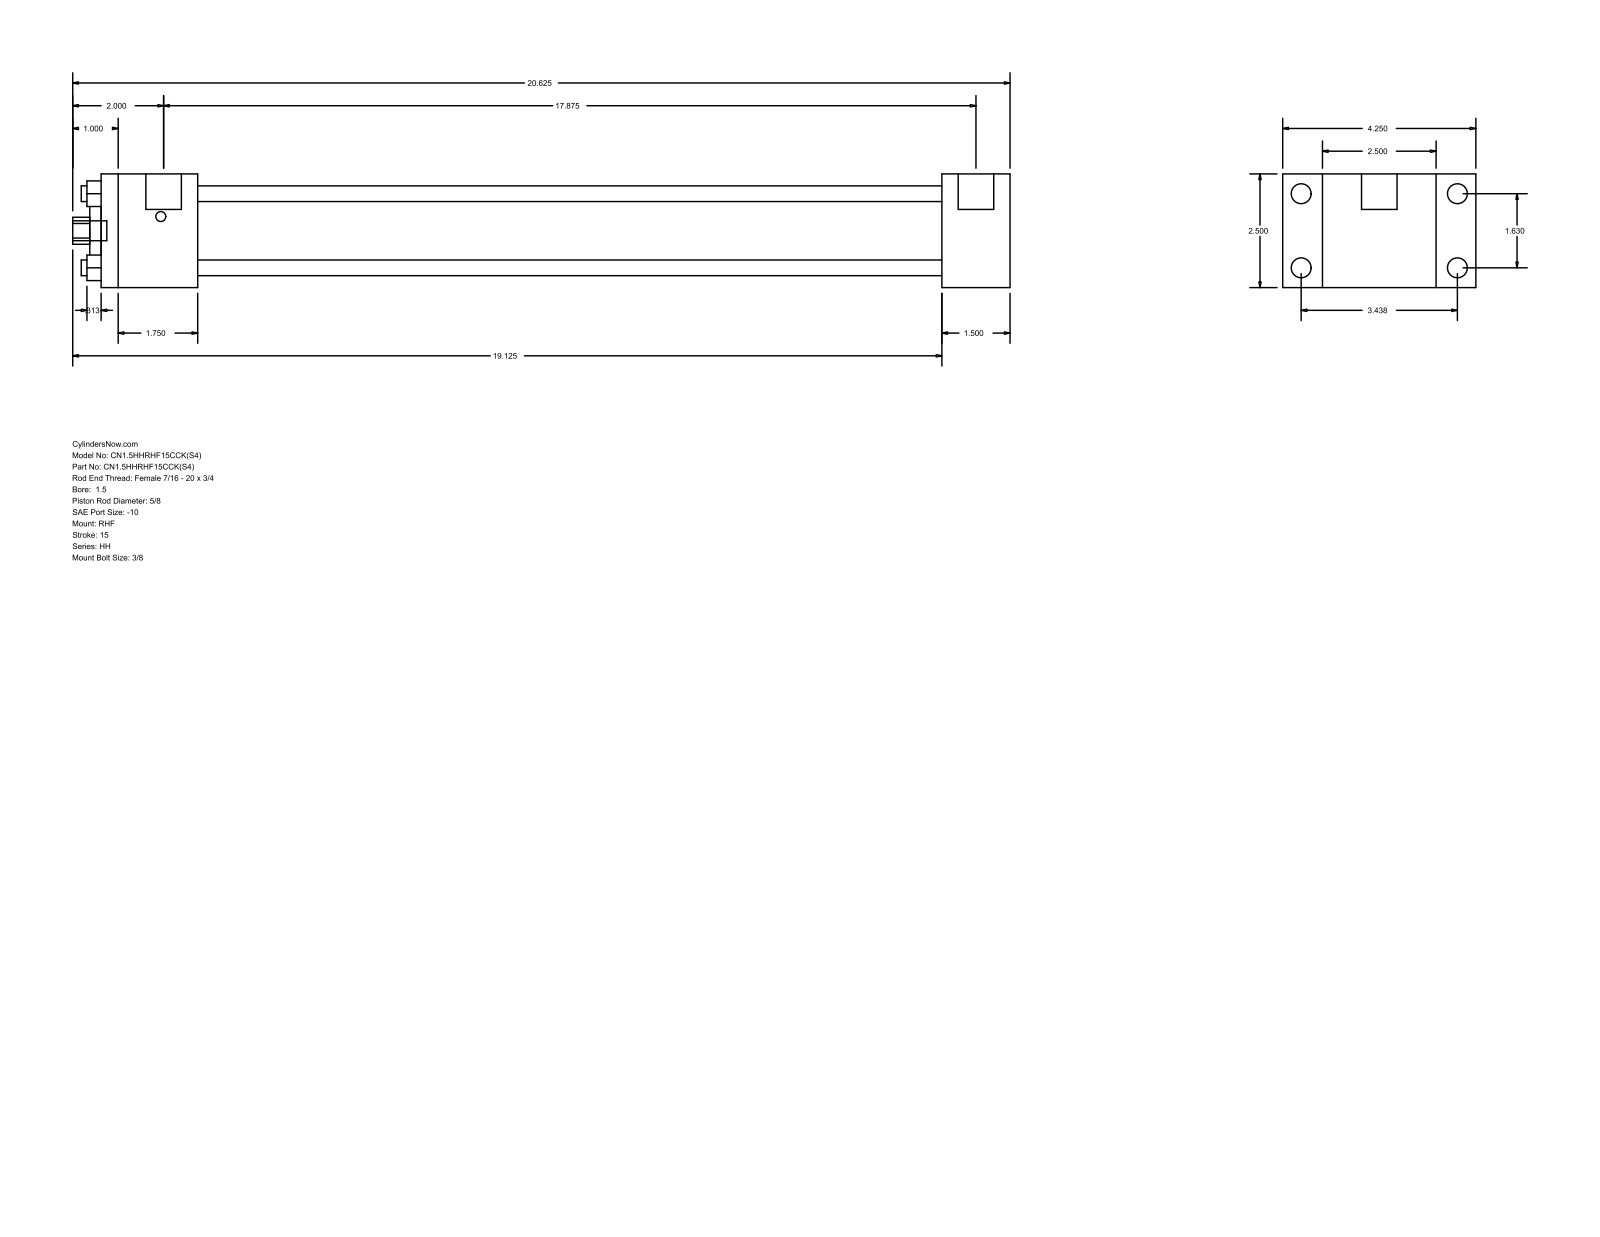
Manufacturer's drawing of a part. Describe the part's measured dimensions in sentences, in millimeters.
The part is named "HH_RHF__0150_0.625". Its 3-D file was written by "GSSL Pune (CONFIG_CONTROL_DESIGN)". It is 0 solids with 88 faces: 60 planar, 28 cylindrical and 0 other. Overall it measures 523.88 by 107.95 by 63.5 millimeters. Round holes: 4 of diameter 8.76, 1 of diameter 15.88, 1 of diameter 28.57, 1 of diameter 44.45. Round bosses or shafts: 4 of diameter 11.13, 4 of diameter 5.56, 2 of diameter 19.84, 1 of diameter 11.11. Partial cylindrical surfaces (rounded edges, fillets, slot ends): 1 of radius 7.54. The main face-to-face distances are 63.5, 22.23, 85.73, 38.11, 469.89, 508, 107.96, 53.97, 415.92, 454.03. The hole center spacings are 29.27, 41.4, 58.55.
